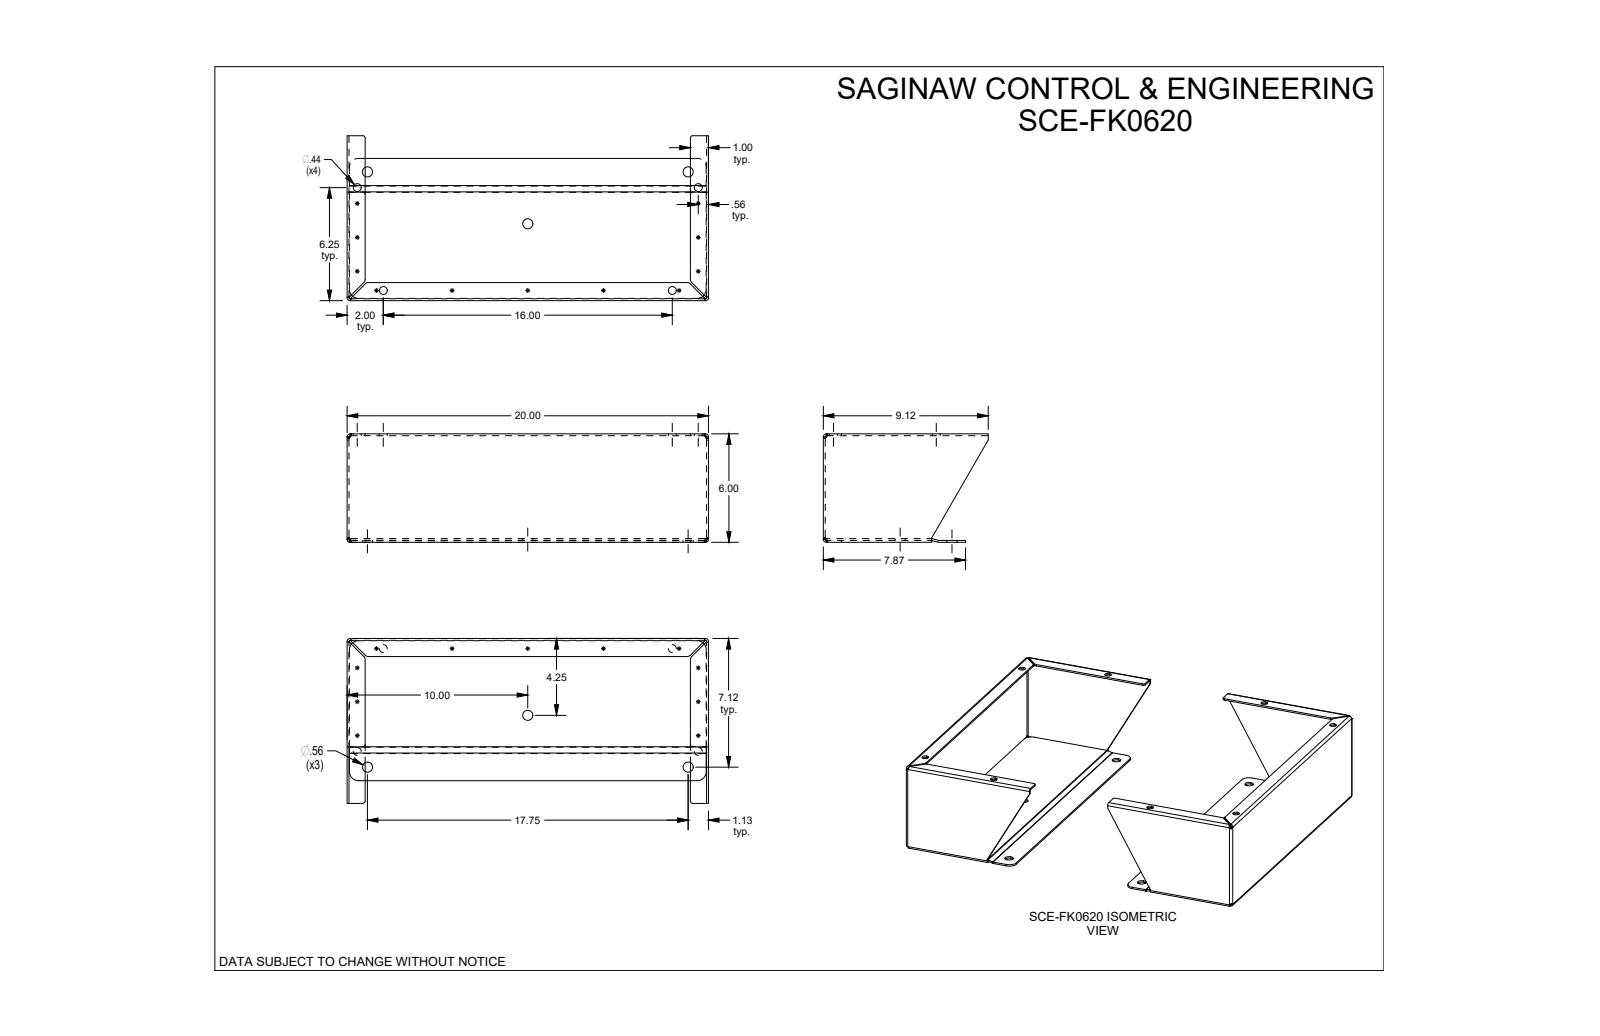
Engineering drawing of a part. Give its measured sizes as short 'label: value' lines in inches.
name: SCE-FK0620
written by: SolidWorks 2019 (CONFIG_CONTROL_DESIGN)
unit: in
bodies: 4 solids, 214 faces (96 planar, 86 cylindrical, 32 other)
size: 24 × 20 × 6
volume: 86.45 in³; area: 1 695 in²
holes: 8× ⌀0.437, 6× ⌀0.563
rounds: 16× R0.166, 12× R0.062, 8× R0.125, 8× R0.22, 8× R0.5, 5× R0.063
face distances: 0.104, 23.896, 19.896, 5.792, 0.101, 5.893, 24, 23.792, 5.896, 20
hole spacings: 1.035, 5.866, 6.614, 8.809, 9.647, 10.646, 16.343, 16.47
